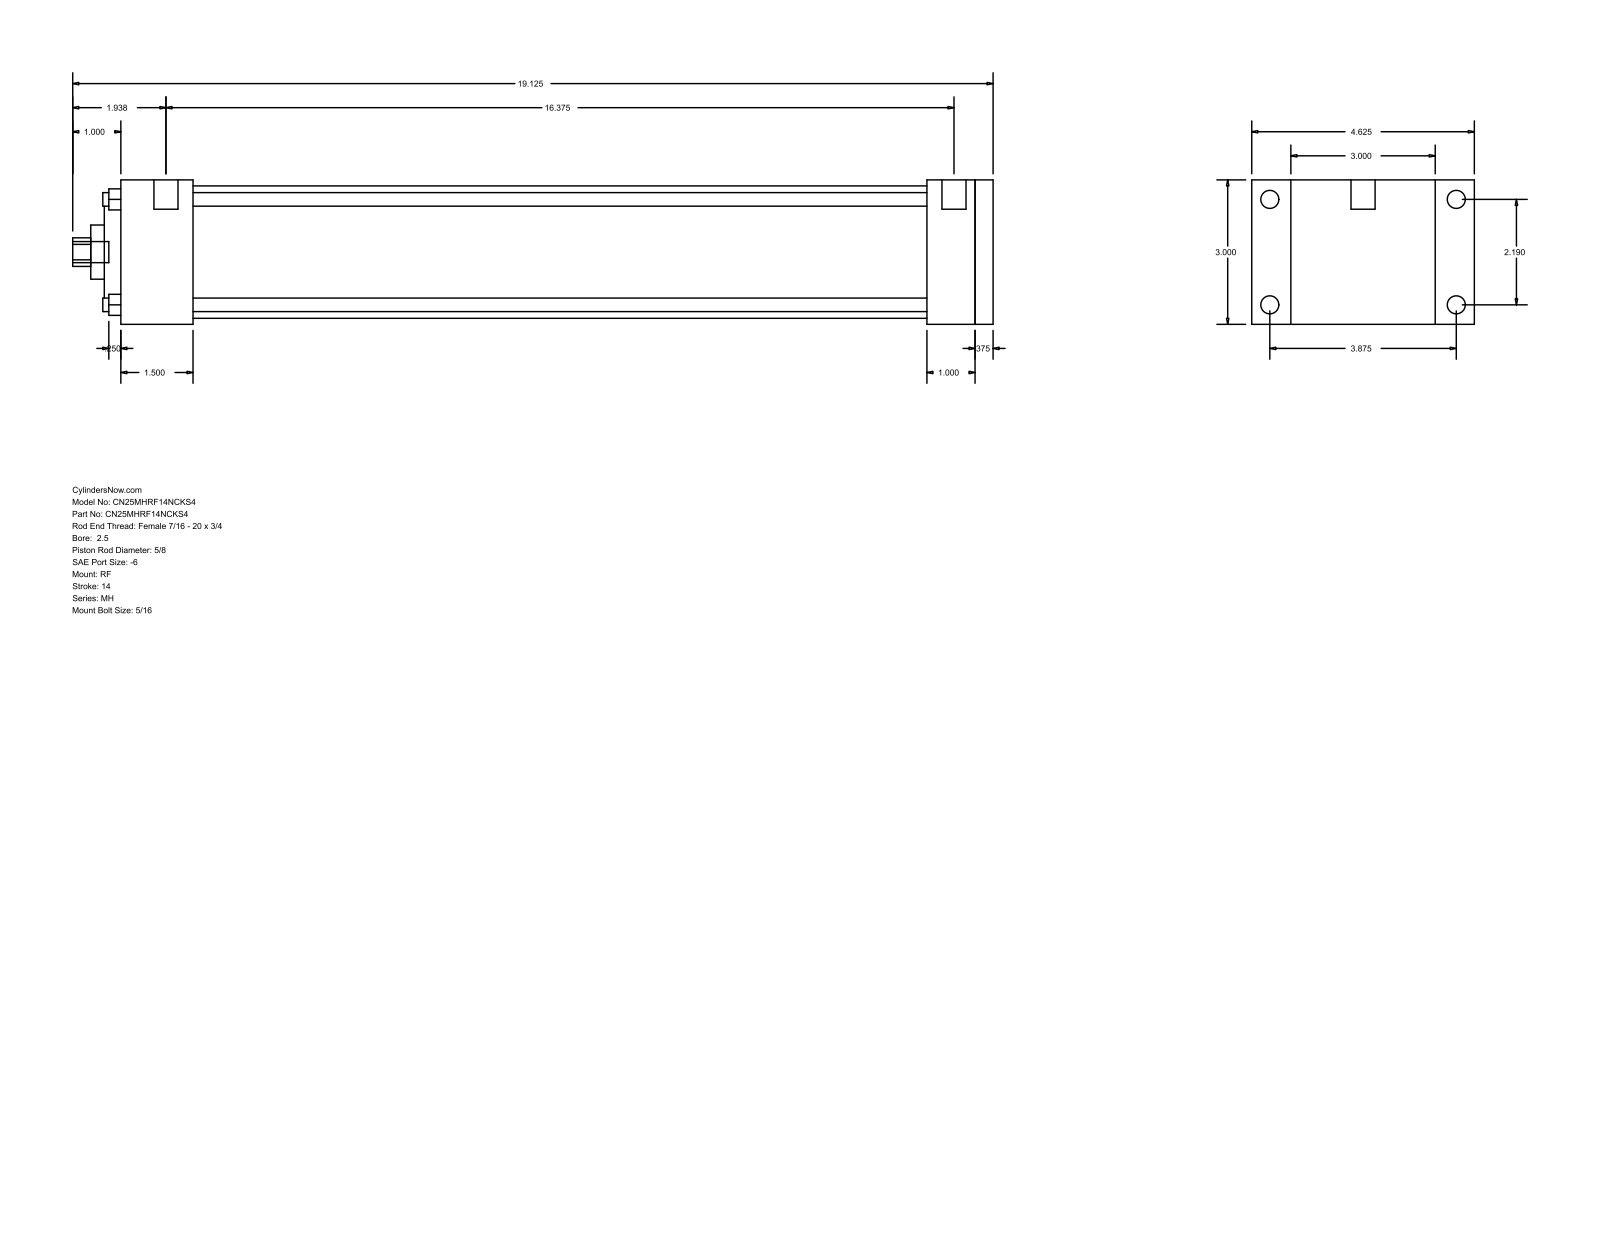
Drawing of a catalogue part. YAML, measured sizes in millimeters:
part_name: "MH_RF__0250_0.625"
step_written_by: "GSSL Pune (CONFIG_CONTROL_DESIGN)"
units: millimeters
bodies: {solids: 0, faces: 94, planar: 65, cylindrical: 29, other: 0}
overall_size: [485.77, 117.47, 76.2]
round_holes:
  - {diameter: 7.14, count: 4}
  - {diameter: 15.88, count: 1}
  - {diameter: 28.57, count: 1}
  - {diameter: 55.55, count: 1}
  - {diameter: 69.85, count: 1}
round_bosses_or_shafts:
  - {diameter: 9.53, count: 4}
  - {diameter: 5.56, count: 4}
  - {diameter: 12.7, count: 2}
  - {diameter: 11.11, count: 1}
partial_cylinders:
  - {radius: 7.54, count: 1}
face_to_face_distances: [76.2, 9.52, 460.37, 450.85, 25.4, 425.45, 34.92, 38.1, 387.35, 412.75]
hole_center_spacings: [39.33, 55.62, 78.66]
